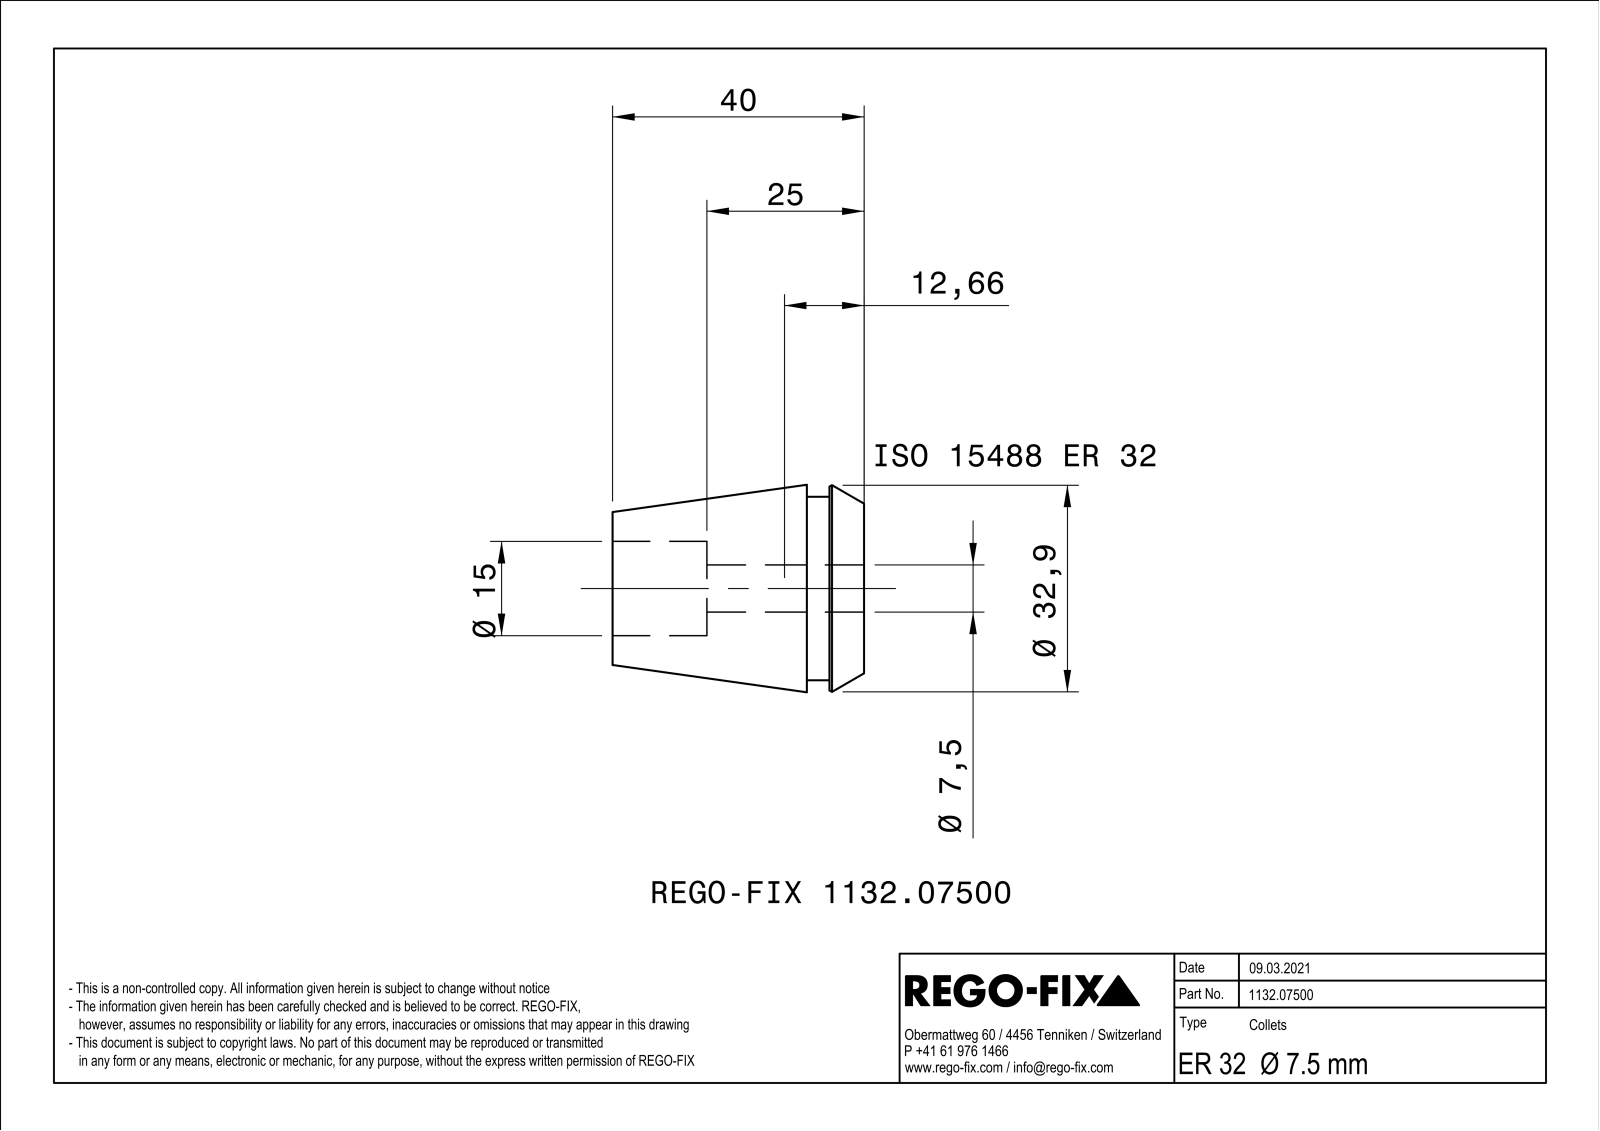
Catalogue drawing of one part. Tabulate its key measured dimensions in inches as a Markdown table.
| quantity | value |
| --- | --- |
| part name | NOCUT |
| STEP written by | SIEMENS PLM Software Solid Edge ST10 (AUTOMOTIVE_DESIGN) |
| units | inches |
| bodies | 1 solid, 256 faces (88 planar, 48 cylindrical, 120 other) |
| overall size | 1.575 × 1.299 × 1.299 |
| volume | 1.165 in³ |
| surface area | 22.33 in² |
| round holes (diameter × count) | 0.591 × 1 |
| round bosses / shafts (diameter × count) | 1.15 × 1 |
| partial cylindrical surfaces (radius × count) | 0.016 × 13, 0.148 × 1 |
| main face-to-face distances | 0.031, 0.032, 0.031, 1.575, 0.358, 1.217, 0.217, 0.142, 1.358, 0.984 |
